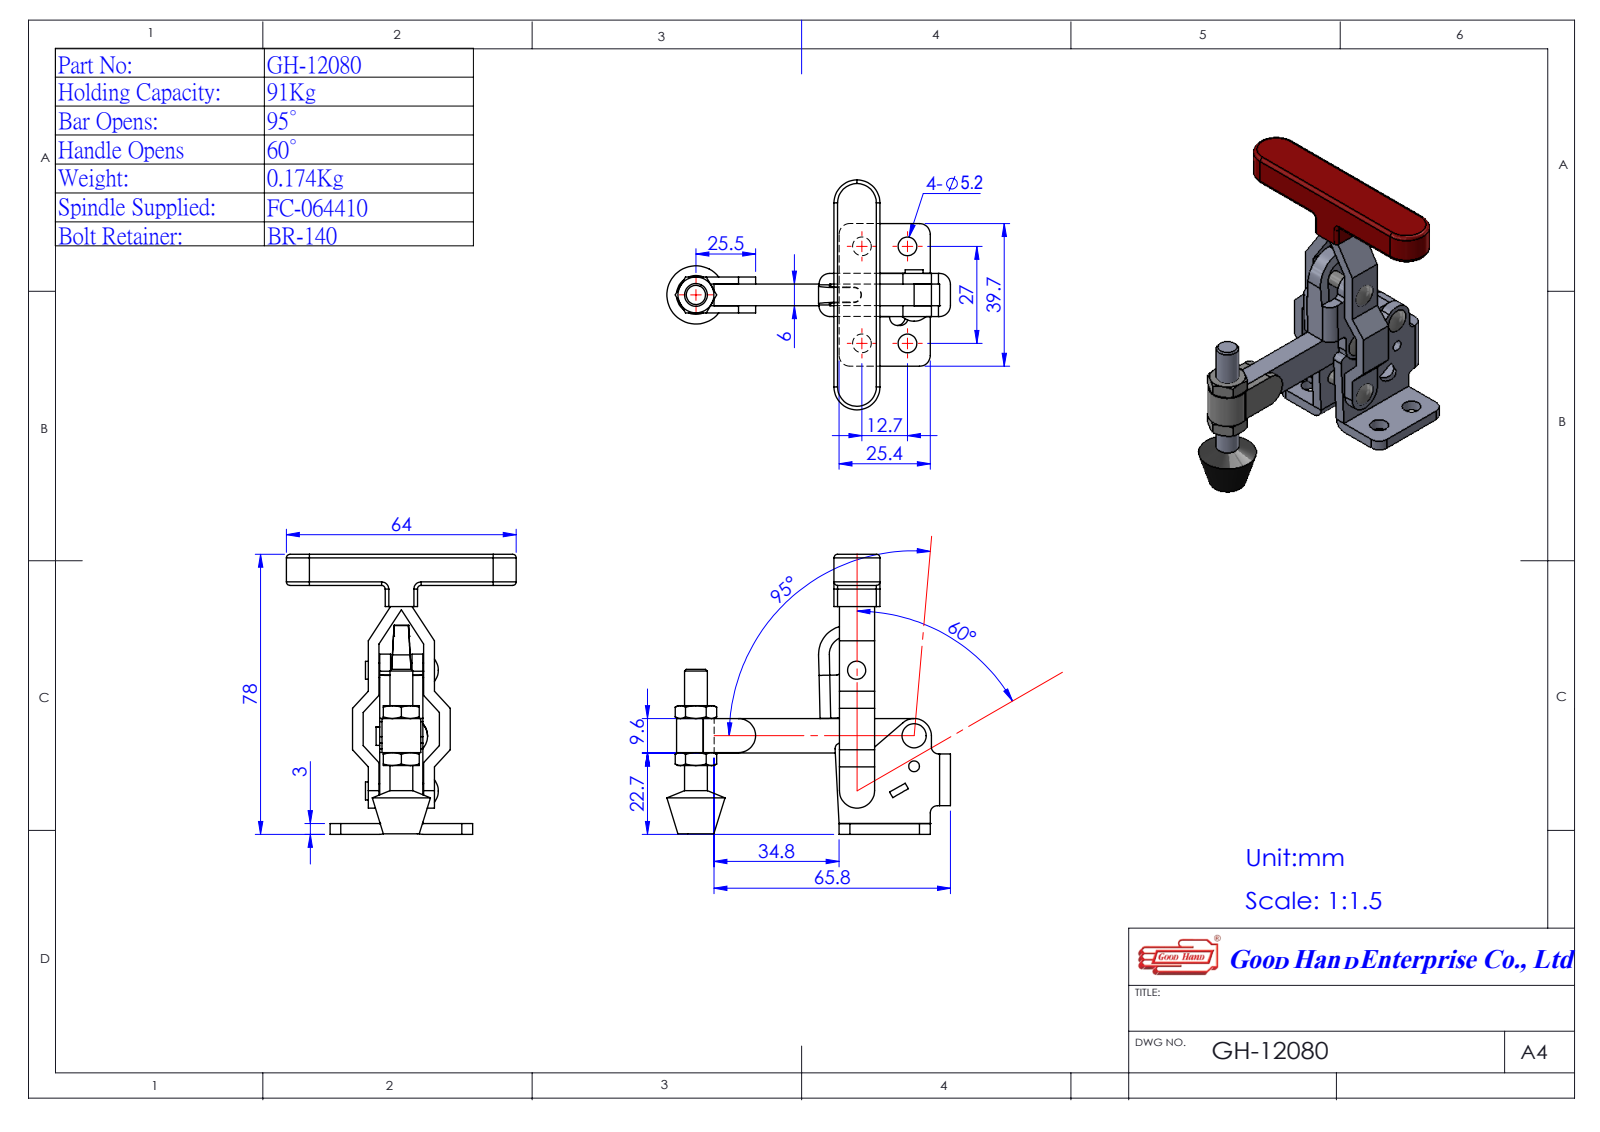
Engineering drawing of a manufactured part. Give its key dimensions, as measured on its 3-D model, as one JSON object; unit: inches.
{"part_name": "11206008_00-1^GH-12080(簡化)-1; Group2^GH-12080(簡化)-1; Group3^GH-12080(簡化)-1; Group5^GH-12080(簡化)-1 (+2 more)", "step_written_by": "SolidWorks 2016 (AUTOMOTIVE_DESIGN)", "units": "inches", "bodies": {"solids": 5, "faces": 250, "planar": 121, "cylindrical": 107, "other": 22}, "overall_size": [3.085, 3.055, 2.52], "volume_in3": 1.718, "surface_area_in2": 29.5, "round_holes": [[0.118, 4], [0.205, 4]], "round_bosses_or_shafts": [[0.197, 4], [0.25, 1]], "partial_cylinders_radius": [[0.118, 4], [0.039, 2], [0.079, 2], [0.08, 2], [0.177, 2], [0.197, 2], [0.252, 2], [0.059, 1]], "face_to_face_distances": [0.118, 0.354, 0.236, 0.472, 0.059, 0.126, 0.48, 0.445, 0.347, 0.504], "hole_center_spacings": [0.5, 1.063, 1.175, 0.603, 0.606, 0.725, 0.87, 0.961]}
